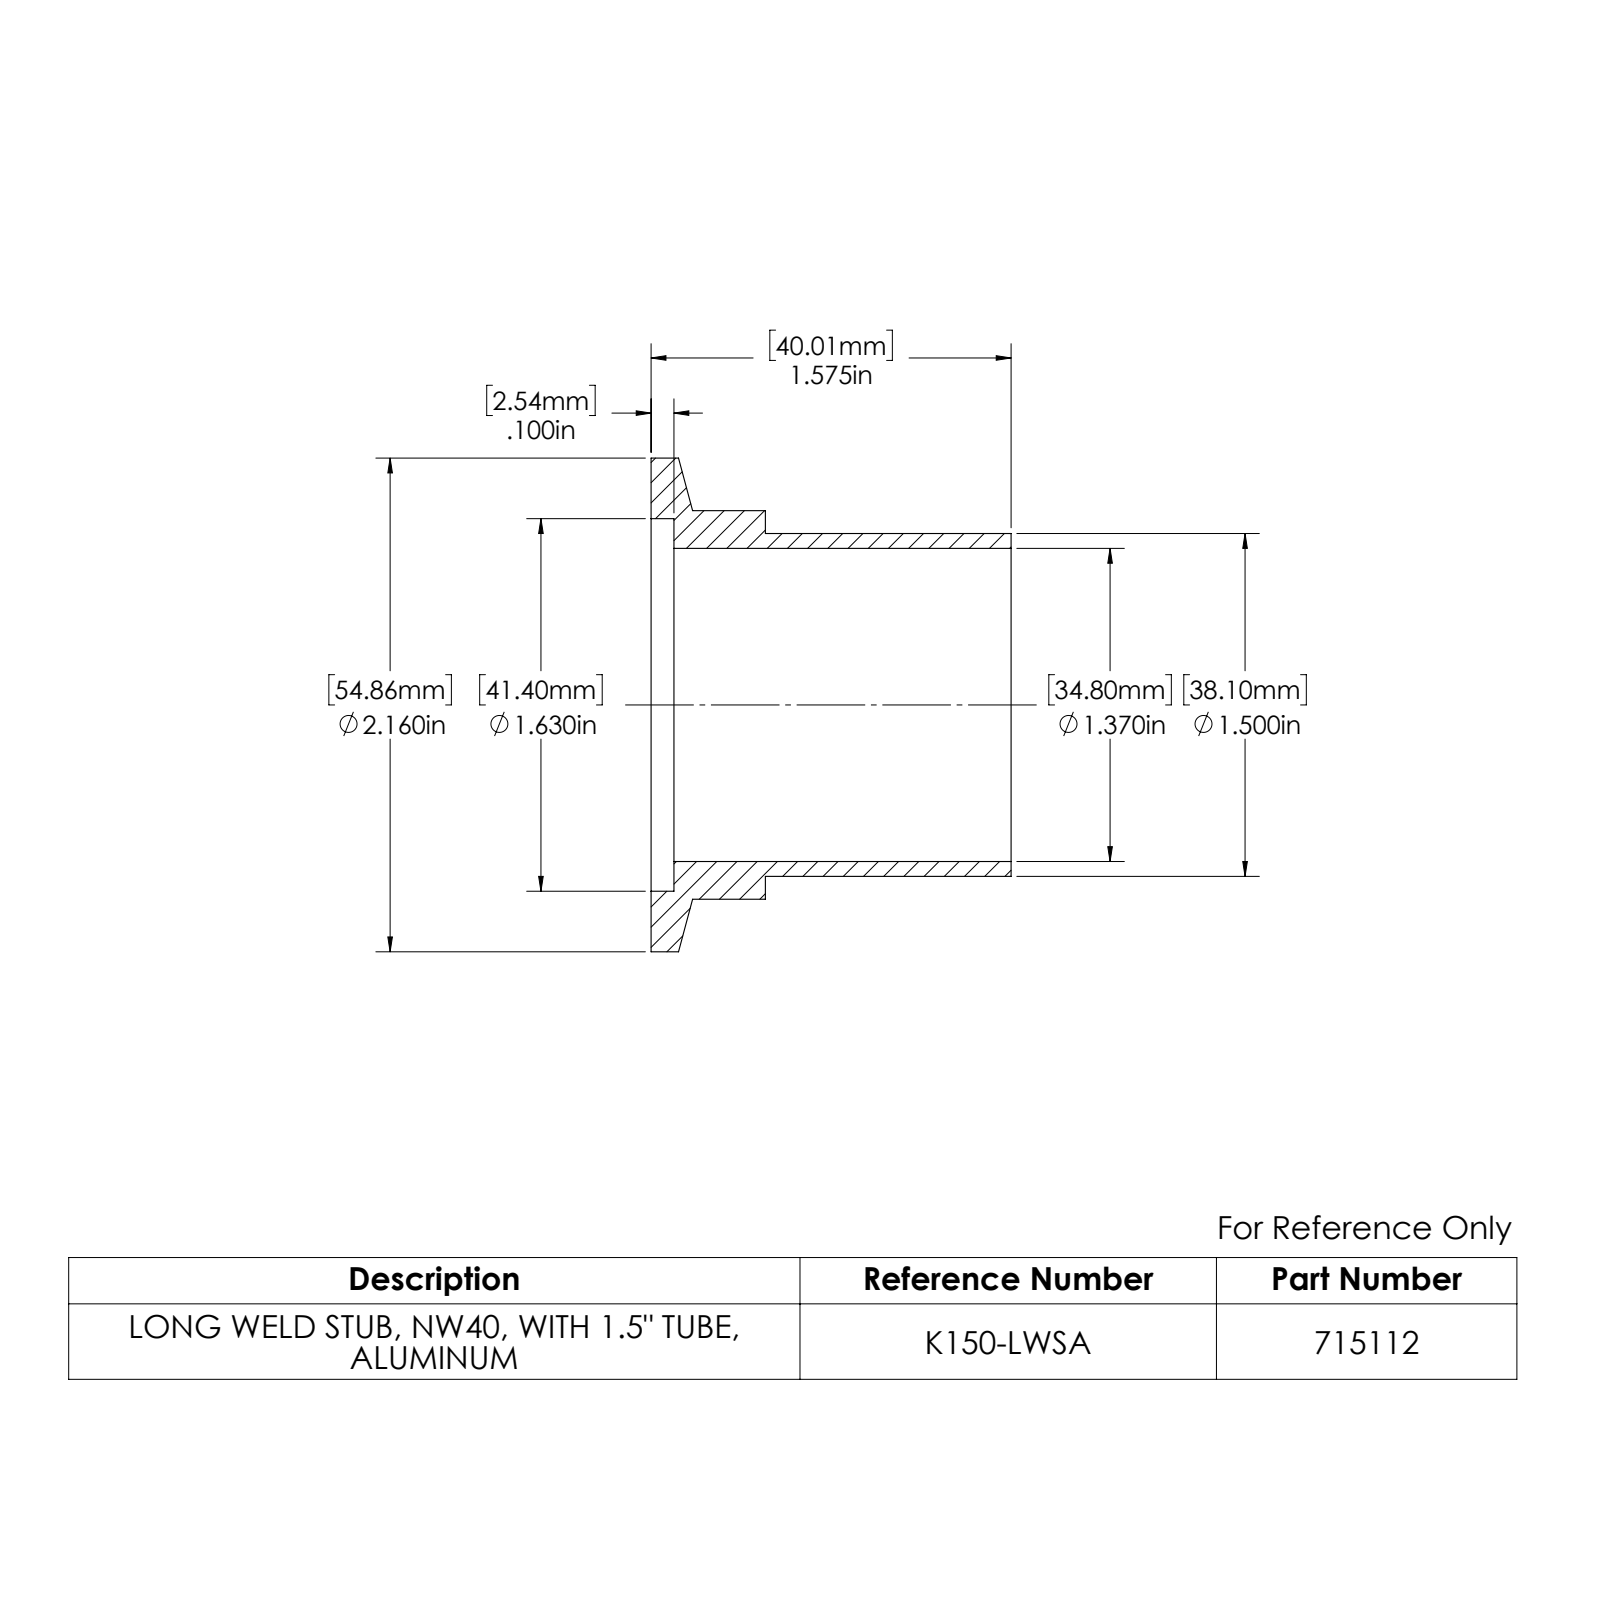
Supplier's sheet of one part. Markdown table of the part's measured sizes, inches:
| quantity | value |
| --- | --- |
| part name | 715112 |
| STEP written by | SolidWorks 2022 (AUTOMOTIVE_DESIGN) |
| units | inches |
| bodies | 1 solid, 16 faces (4 planar, 10 cylindrical, 2 other) |
| overall size | 2.16 × 2.16 × 1.575 |
| volume | 0.86 in³ |
| surface area | 18.87 in² |
| round holes (diameter × count) | 1.37 × 1, 1.63 × 1 |
| round bosses / shafts (diameter × count) | 2.16 × 1, 1.7 × 1, 1.5 × 1 |
| main face-to-face distances | 0.1, 0.5, 0.4, 1.575, 1.475, 1.075 |
